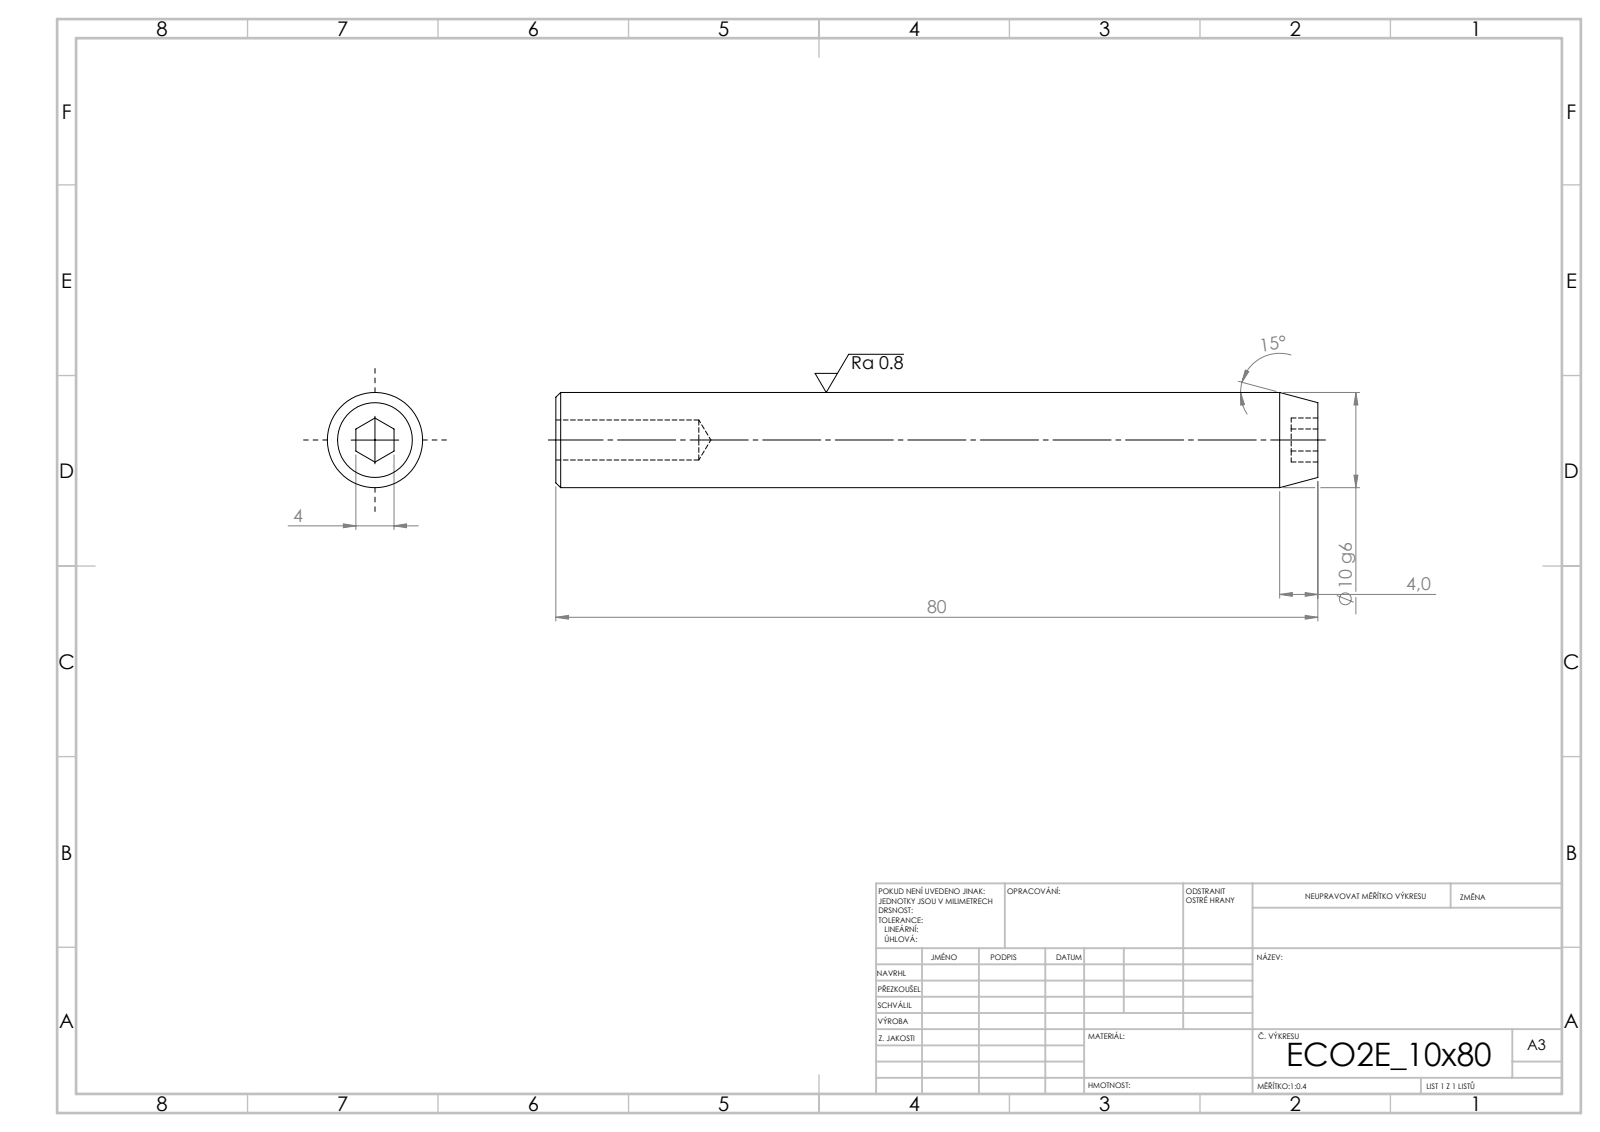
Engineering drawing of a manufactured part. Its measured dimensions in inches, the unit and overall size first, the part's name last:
Units: inches
Overall size (bounding box): 3.15 × 0.394 × 0.394
Round holes (diameter × count): ⌀0.165 ×1
Round bosses / shafts (diameter × count): ⌀0.394 ×1
Main face-to-face distances: 3.15, 0.157, 0.11, 3.039
Volume: 0.364 in³ · Surface area: 4.433 in²
Bodies: 1 solid, 19 faces (9 planar, 4 cylindrical, 6 other)
STEP written by: SolidWorks 2019 (CONFIG_CONTROL_DESIGN)
